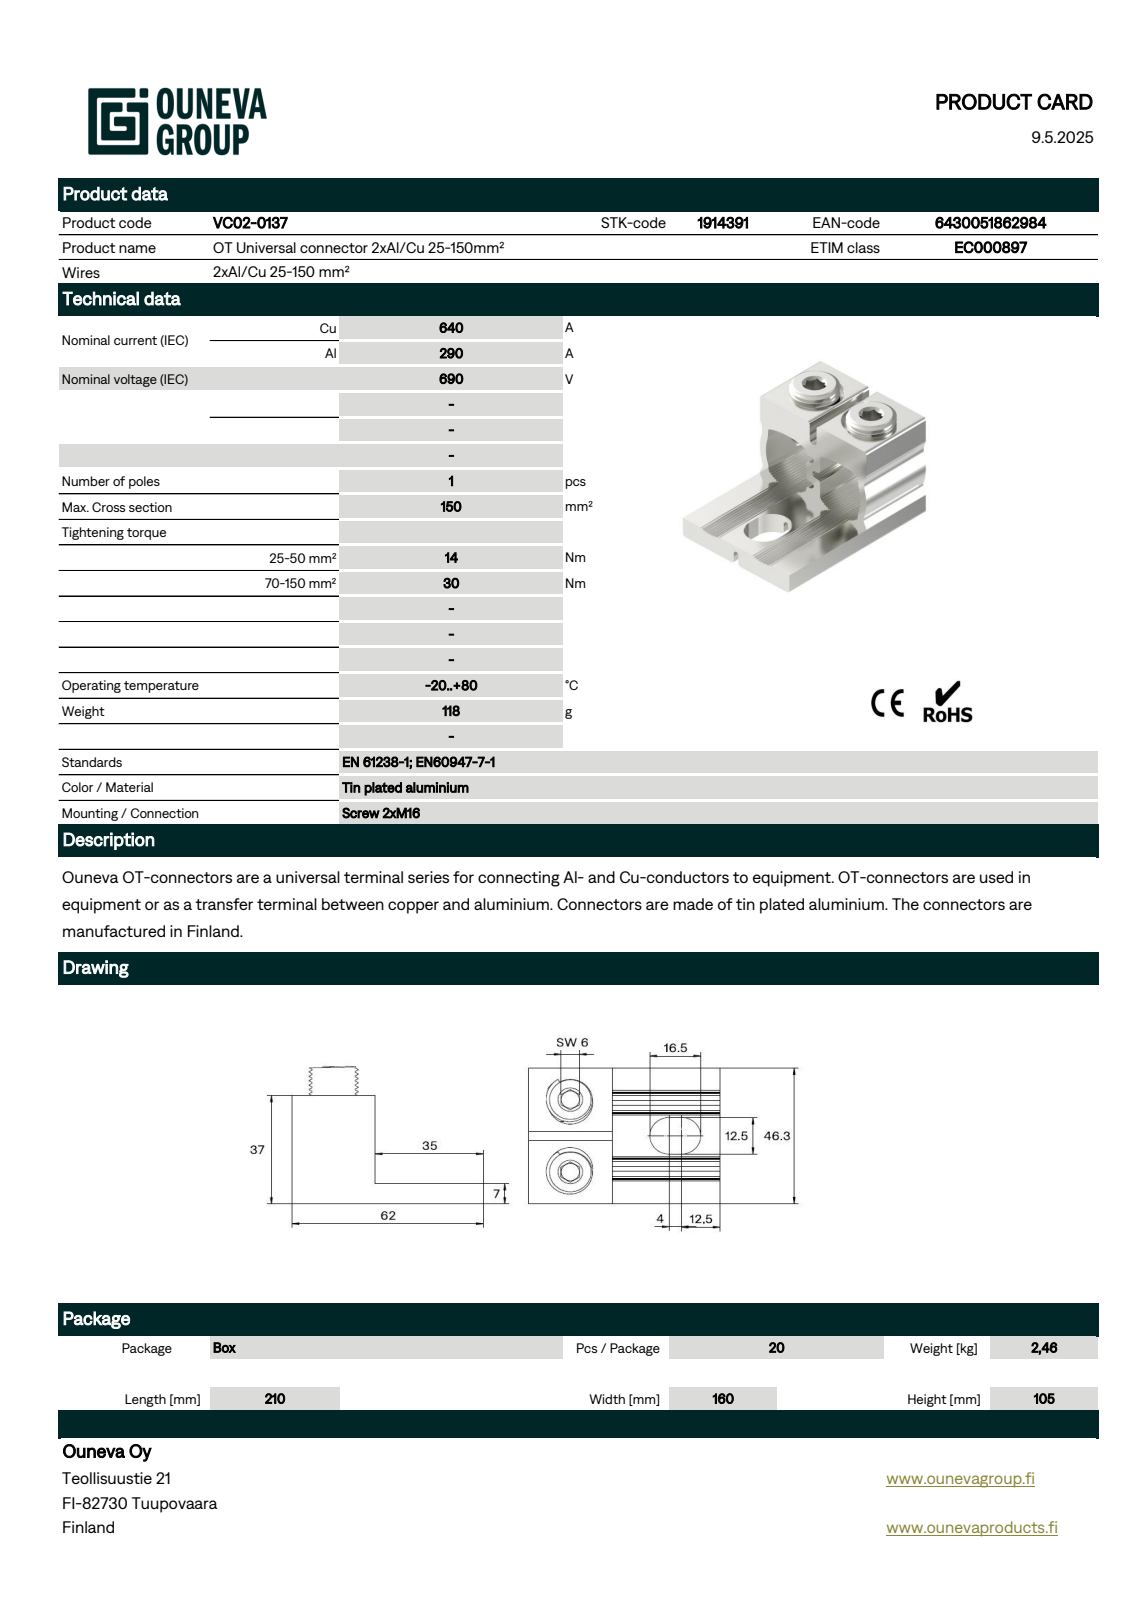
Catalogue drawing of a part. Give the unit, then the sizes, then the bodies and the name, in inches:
Units: inches
Overall size (bounding box): 2.441 × 1.929 × 1.823
Round bosses / shafts (diameter × count): ⌀0.63 ×2
Partial cylindrical surfaces — rounded edges, fillets, slot ends (radius × count): R0.01 ×62, R0.006 ×20, R0.039 ×15, R0.049 ×7, R0.089 ×4, R0.134 ×2, R0.236 ×2, R0.246 ×2
Main face-to-face distances: 0.276, 1.457, 1.181, 1.063, 1.823, 0.098, 2.441, 1.378, 0.852, 0.97
Volume: 2.462 in³ · Surface area: 26.74 in²
Bodies: 1 solid, 208 faces (64 planar, 132 cylindrical, 12 other)
Part name (STEP PRODUCT): Liitinrunko OT 2x150
STEP written by: Creo Elements/Direct Modeling 20.6A 14-Oct-2023 (C) Parametric Technology GmbH (AUTOMOTIVE_DESIGN)
